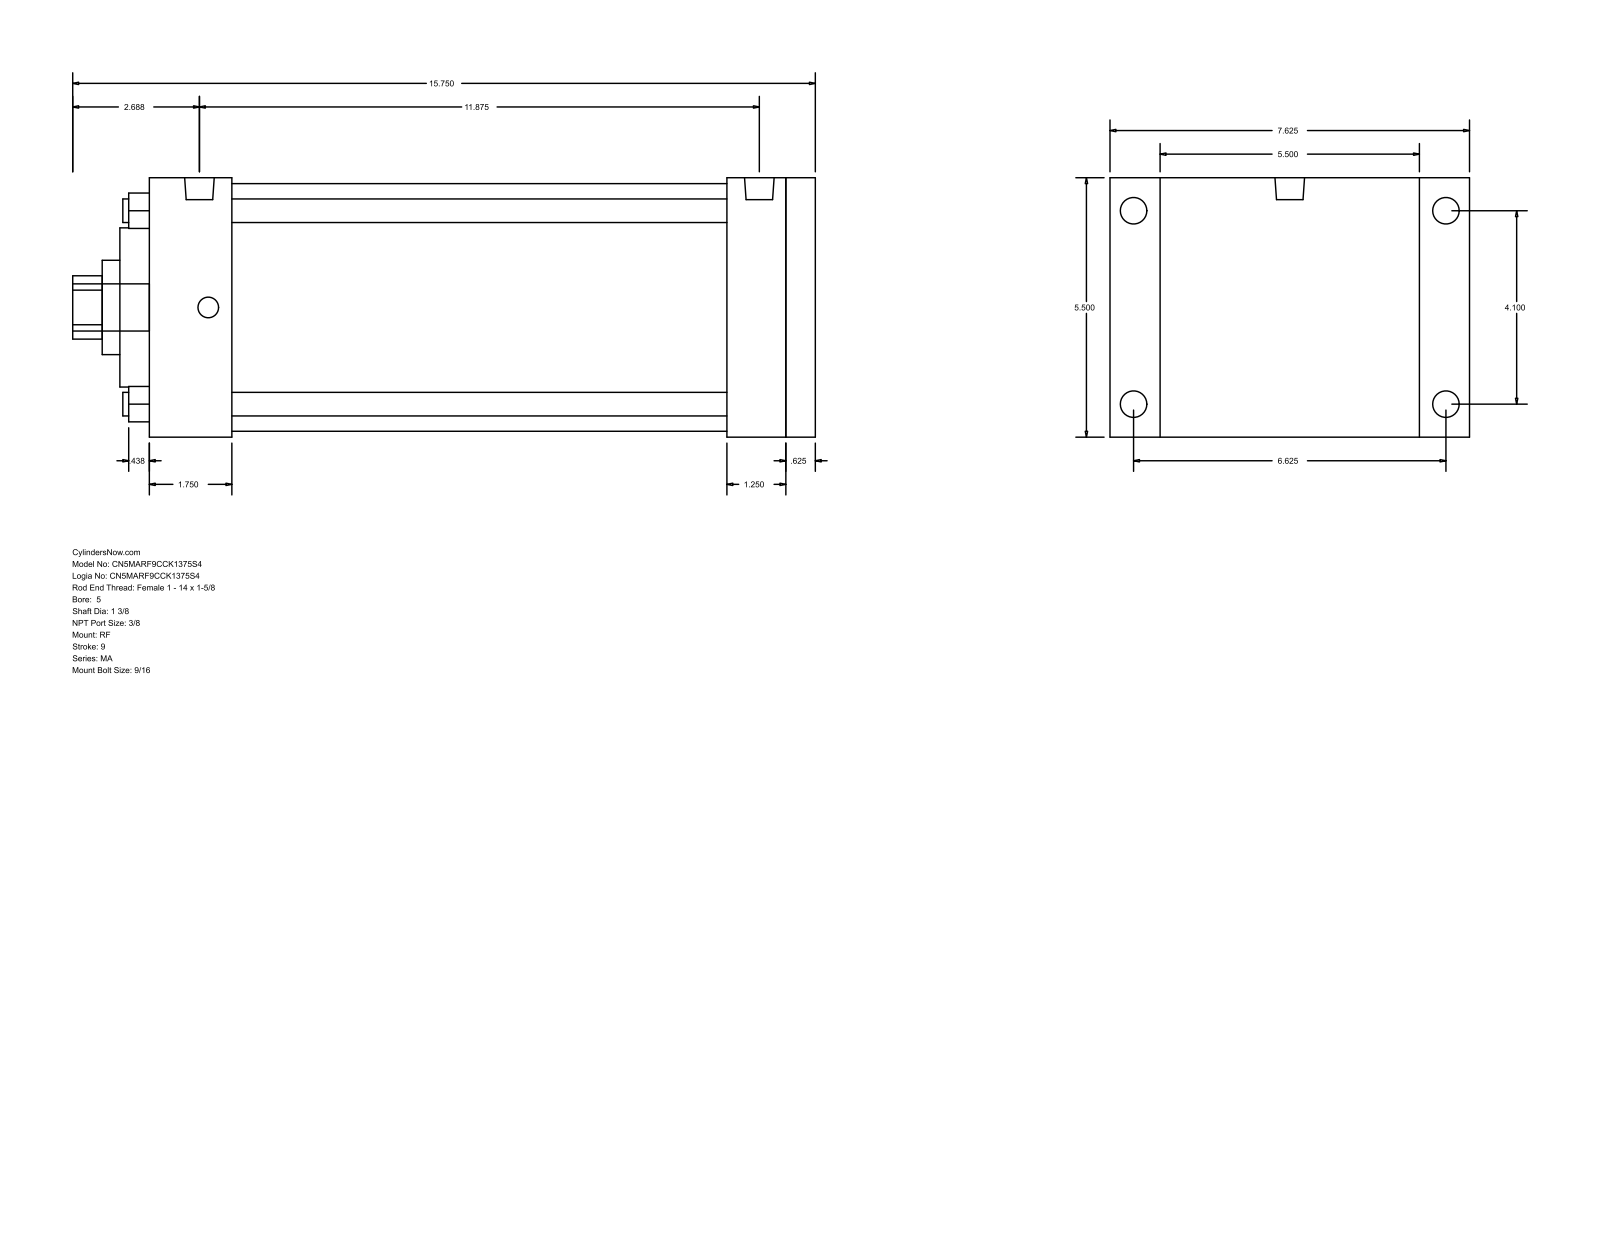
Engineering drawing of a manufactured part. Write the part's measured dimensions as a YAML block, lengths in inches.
part_name: "MA_RF__0500_1.375"
step_written_by: "GSSL Pune (CONFIG_CONTROL_DESIGN)"
units: inches
bodies: {solids: 0, faces: 94, planar: 65, cylindrical: 29, other: 0}
overall_size: [15.75, 7.625, 5.5]
round_holes:
  - {diameter: 0.5, count: 4}
  - {diameter: 1.375, count: 1}
  - {diameter: 2, count: 1}
  - {diameter: 3.375, count: 1}
  - {diameter: 5.25, count: 1}
round_bosses_or_shafts:
  - {diameter: 0.563, count: 4}
  - {diameter: 0.437, count: 4}
  - {diameter: 0.627, count: 2}
  - {diameter: 1, count: 1}
partial_cylinders:
  - {radius: 0.672, count: 1}
face_to_face_distances: [5.5, 14.125, 0.625, 13.5, 1.75, 11.75, 12.375, 12.25, 10.5, 1.25]
hole_center_spacings: [2.899, 4.1, 5.798]
